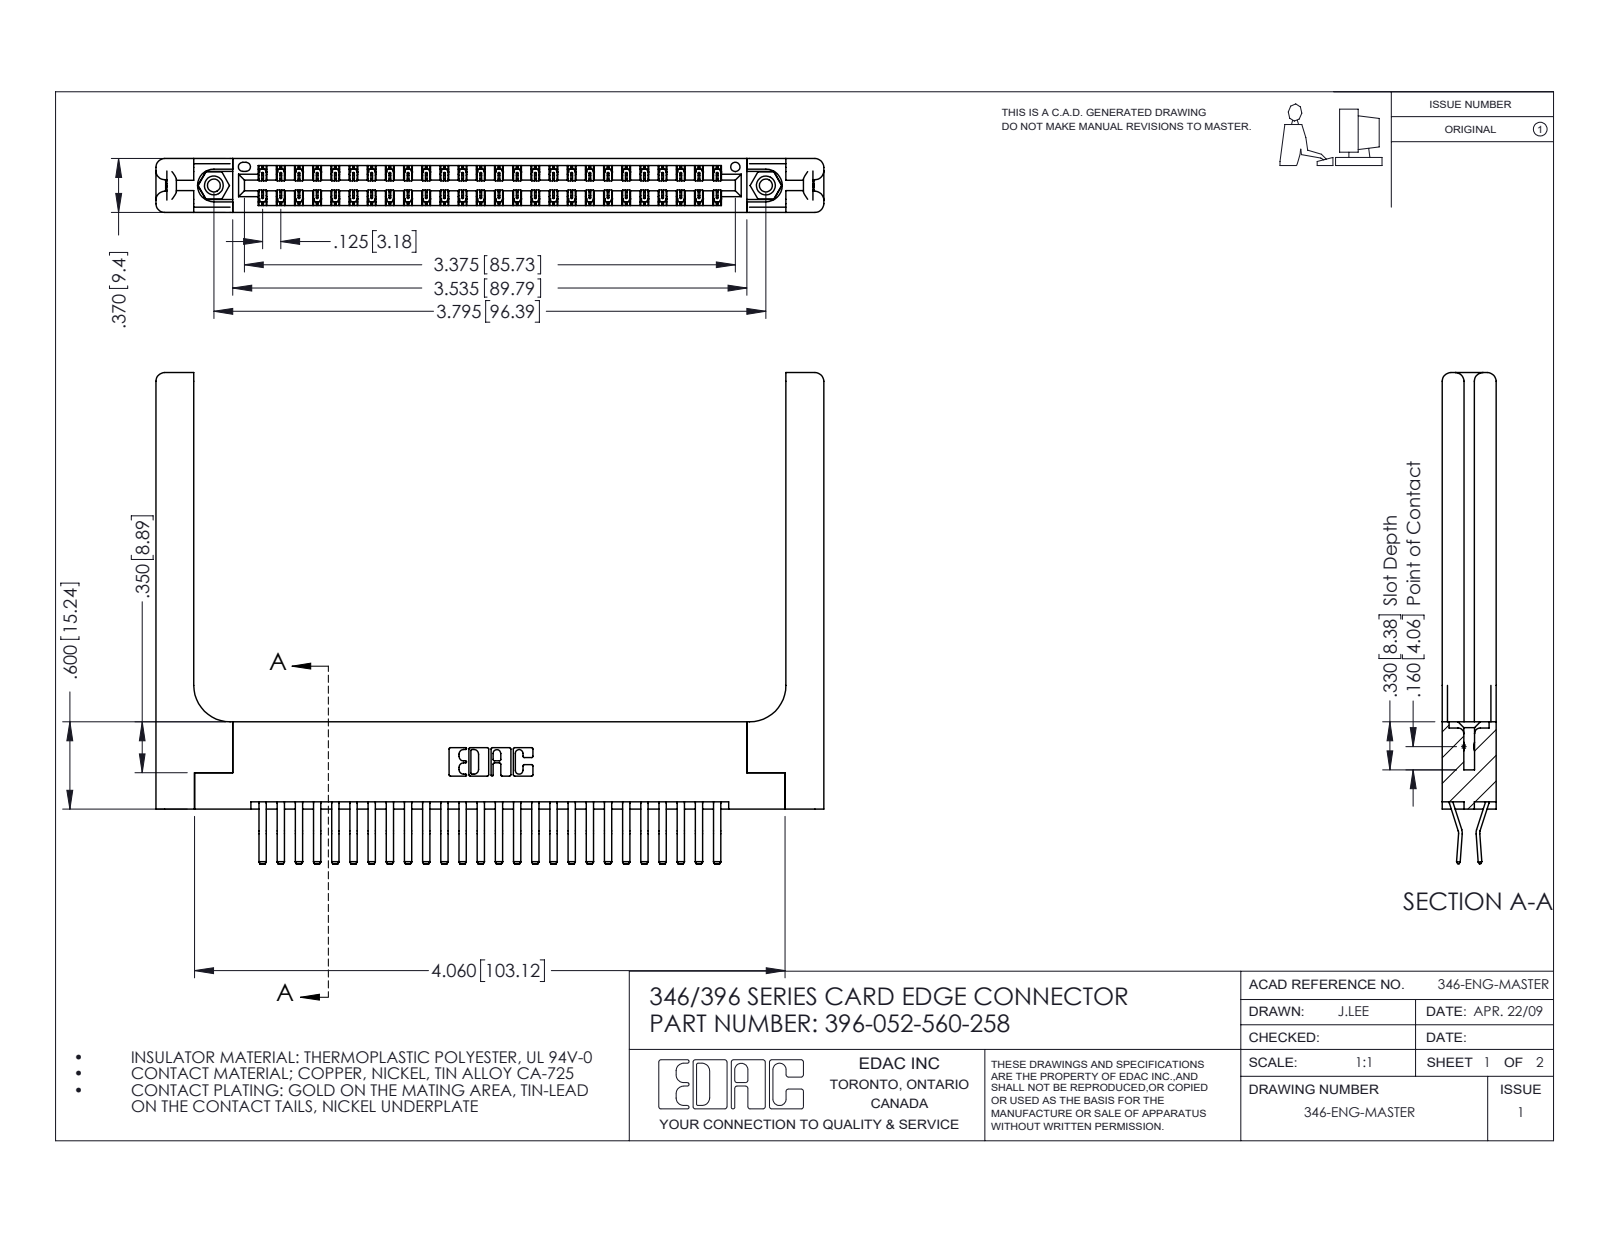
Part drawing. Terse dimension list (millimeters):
name: 346-220-058_345-220-058; 396-052-560-258; 345-250-001_345-250-001-102; 345-292-001_560 Tail (+1 more)
written by: SolidWorks 2016 (CONFIG_CONTROL_DESIGN)
unit: mm
bodies: 57 solids, 3186 faces (2044 planar, 1082 cylindrical, 60 other)
size: 116.6 × 85.7 × 9.4
volume: 19 070 mm³; area: 21 560 mm²
holes: 2× ⌀2.3, 2× ⌀3.2, 2× ⌀4, 1× ⌀1.6
bosses: 2× ⌀3.9
rounds: 78× R0.2, 22× R0.3, 16× R1.5, 6× R0.2, 6× R0.8, 3× R0.7, 2× R0.3, 2× R0.4
face distances: 9.4, 1.8, 1.2, 8.2, 3.8, 3.8, 0.6, 6.4, 7.6, 7
hole spacings: 6.2, 91.1, 96.4
